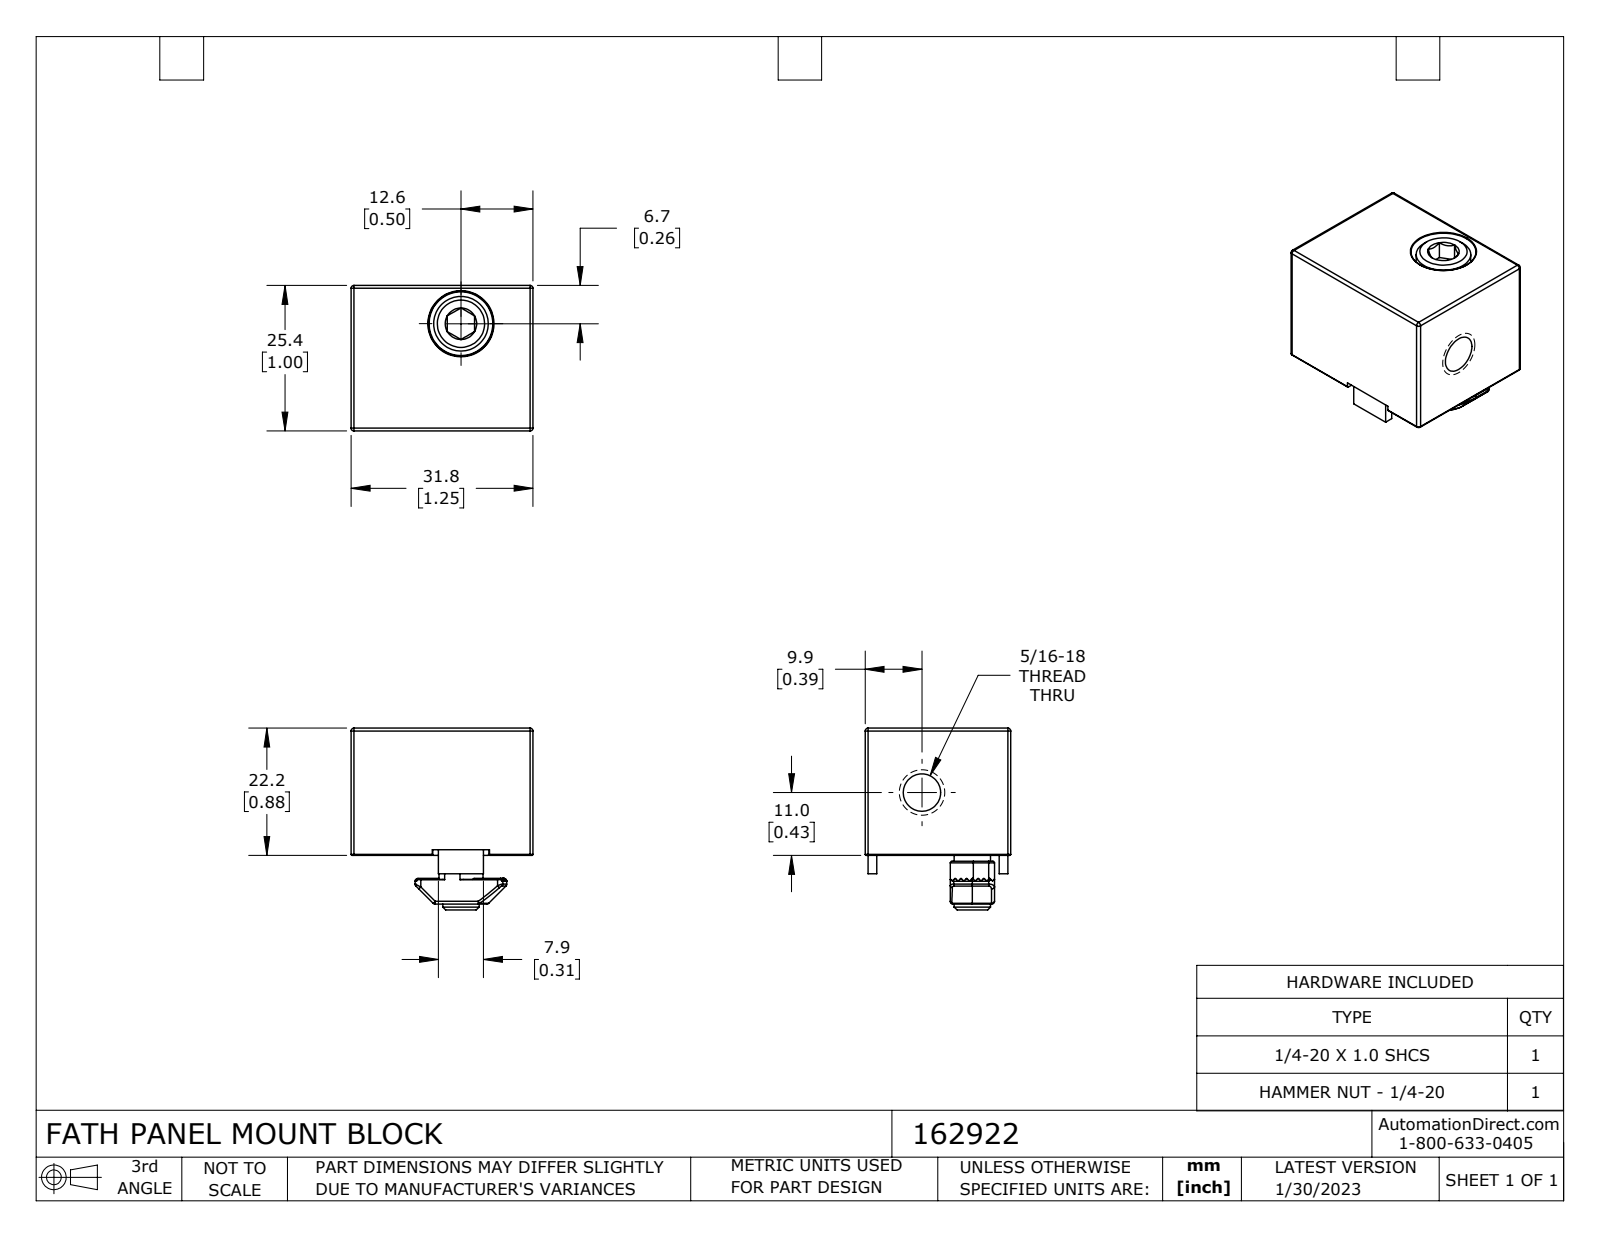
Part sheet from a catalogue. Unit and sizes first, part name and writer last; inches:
Units: inches
Overall size (bounding box): 1.25 × 1.25 × 1
Round holes (diameter × count): ⌀0.187 ×1, ⌀0.257 ×1
Round bosses / shafts (diameter × count): ⌀0.375 ×1, ⌀0.25 ×1
Partial cylindrical surfaces — rounded edges, fillets, slot ends (radius × count): R0.02 ×18, R0.008 ×10, R0.004 ×7, R0.039 ×6, R0.012 ×4, R0.083 ×4, R0.157 ×2, R0.207 ×1
Main face-to-face distances: 0.079, 1, 1.25, 0.921, 1.171, 0.875, 0.843, 0.329, 0.948, 0.302
Volume: 0.812 in³ · Surface area: 12.85 in²
Bodies: 3 solids, 261 faces (110 planar, 101 cylindrical, 50 other)
Part name (STEP PRODUCT): 162922
STEP written by: SolidWorks 2021 (CONFIG_CONTROL_DESIGN)
